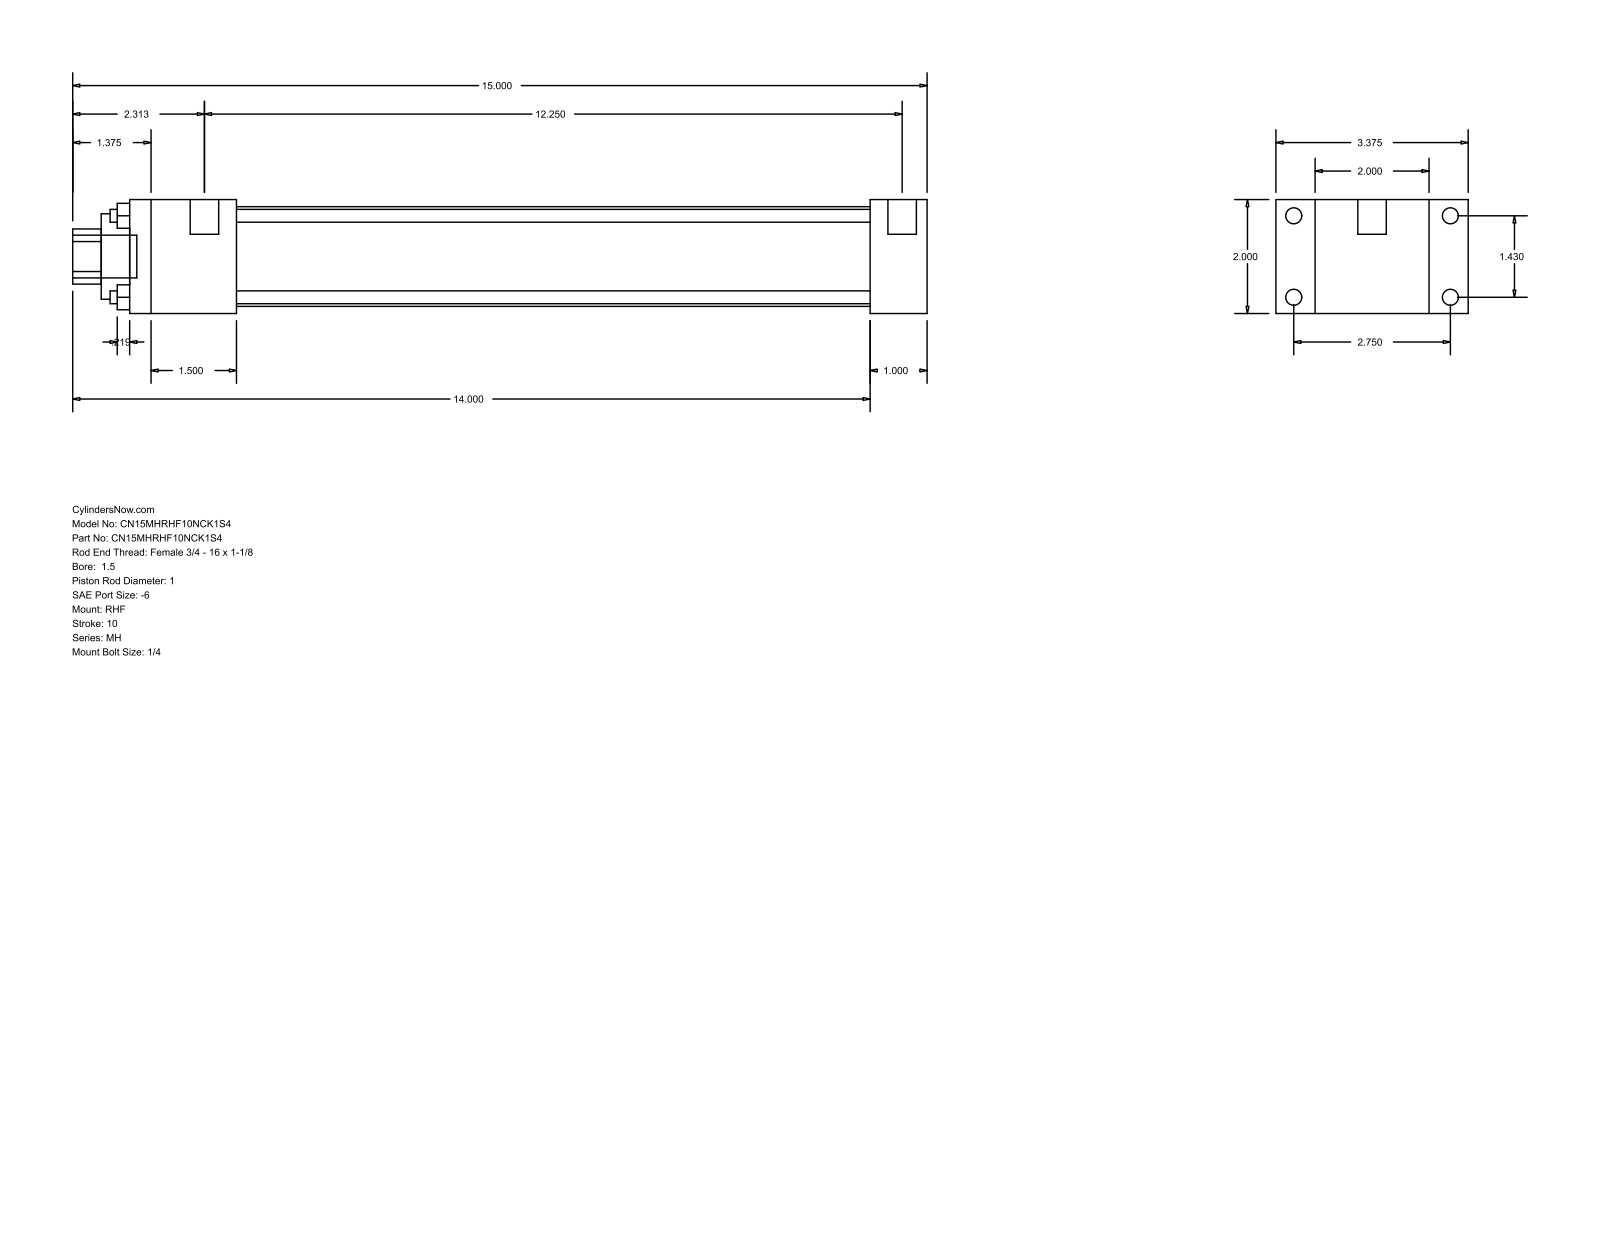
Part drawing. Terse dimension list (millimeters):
name: MH_RHF__0150_1
written by: GSSL Pune (CONFIG_CONTROL_DESIGN)
unit: mm
bodies: 0 solids, 88 faces (60 planar, 28 cylindrical, 0 other)
size: 381 × 85.72 × 50.8
holes: 4× ⌀5.71, 1× ⌀25.4, 1× ⌀38.1, 1× ⌀44.45
bosses: 4× ⌀7.14, 4× ⌀5.56, 2× ⌀12.7, 1× ⌀19.05
rounds: 1× R12.29
face distances: 50.8, 25.4, 17.46, 68.26, 85.72, 355.6, 330.2, 47.63, 282.57, 307.97
hole spacings: 25.68, 36.32, 51.36
